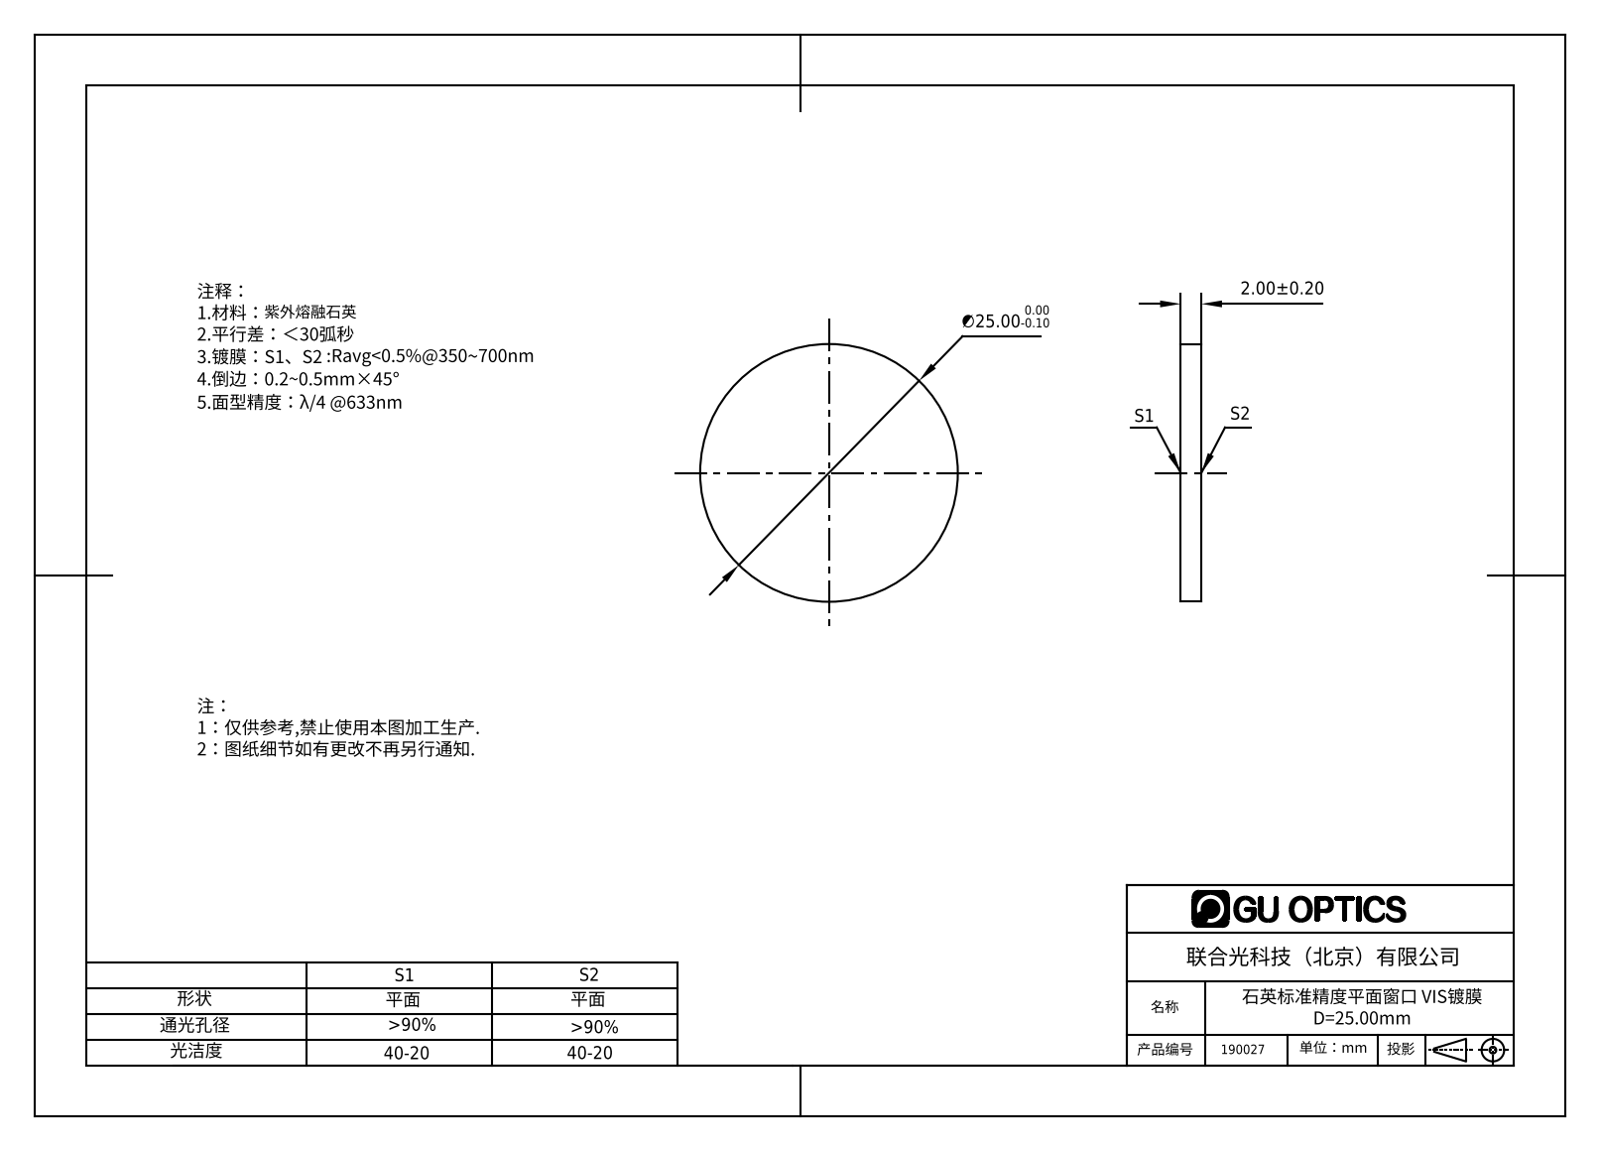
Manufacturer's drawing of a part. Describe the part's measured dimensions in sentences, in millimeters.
The part is named "190005". Its 3-D file was written by "SolidWorks 2016 (AUTOMOTIVE_DESIGN)". It is 1 solid with 4 faces: 2 planar, 2 cylindrical and 0 other. Overall it measures 25 by 25 by 2 millimeters. Its volume is 982 cubic millimeters and its surface area 1 139 square millimeters. Round bosses or shafts: 1 of diameter 25. The main face-to-face distances are 2.
